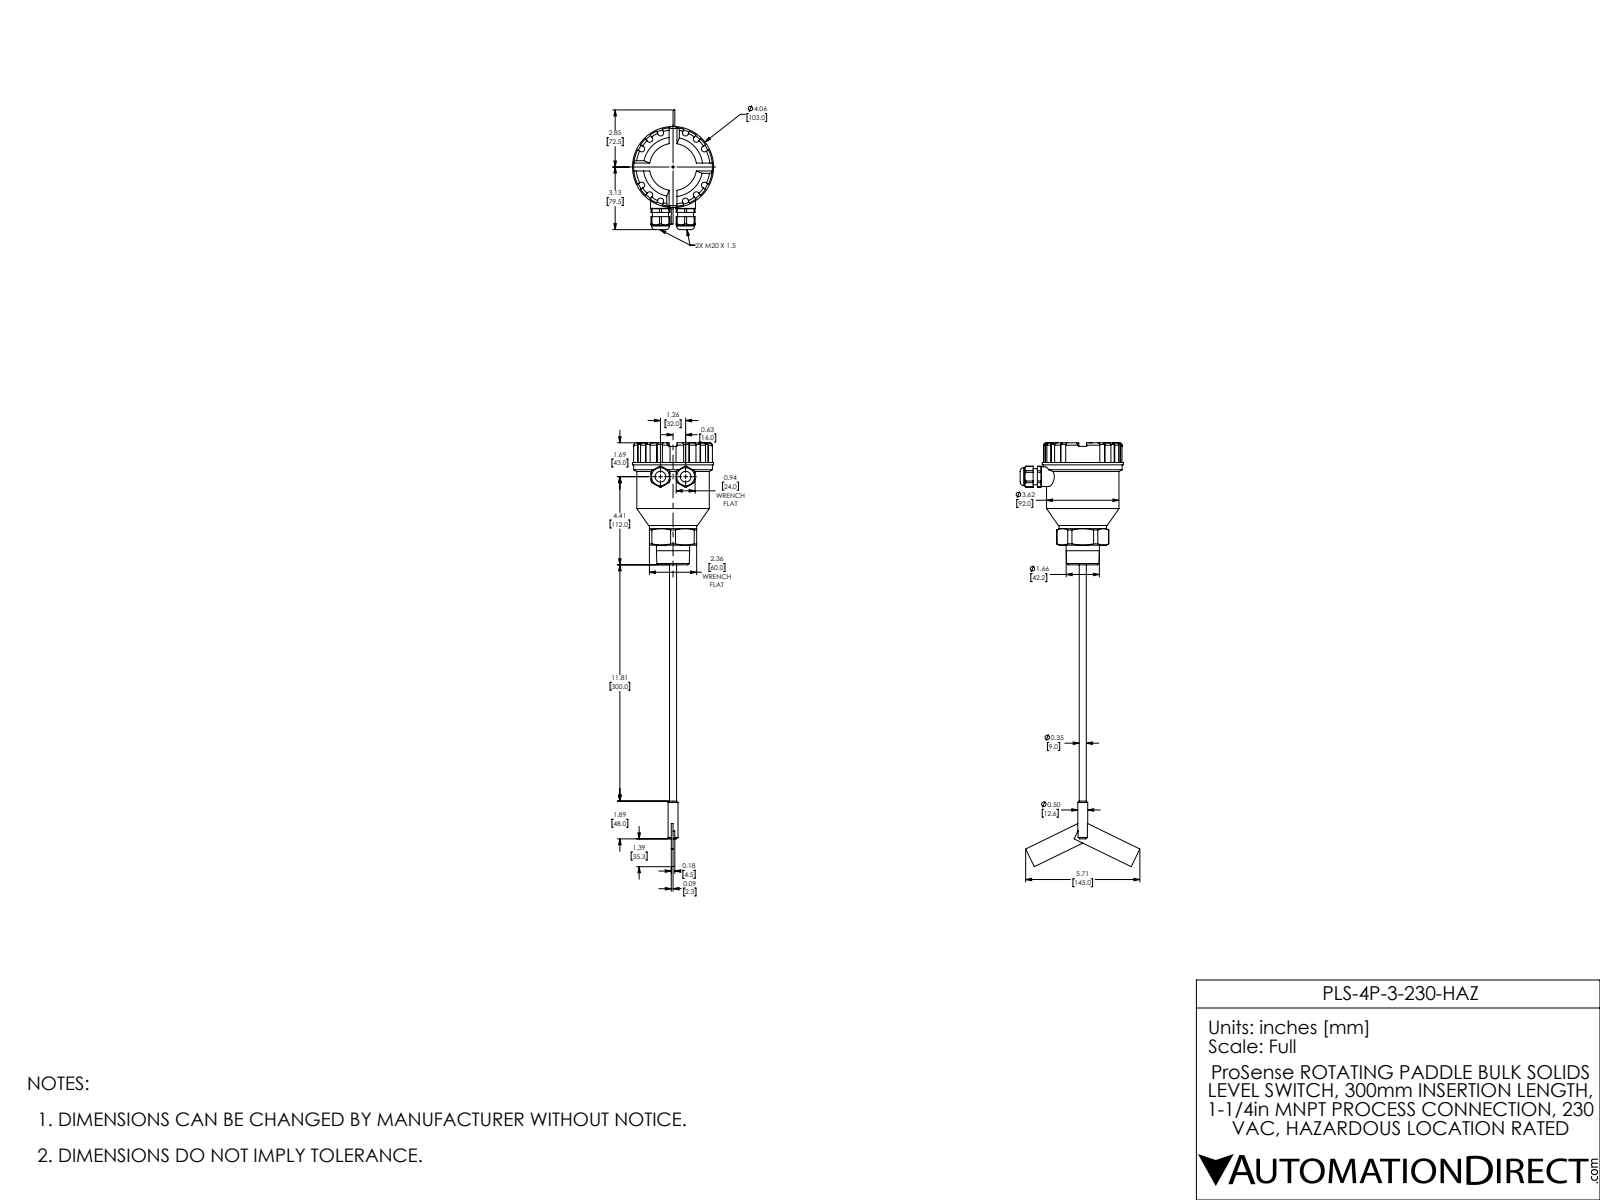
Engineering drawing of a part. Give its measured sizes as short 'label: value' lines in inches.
name: 300mm Shaft NC
written by: SolidWorks 2017 (AUTOMOTIVE_DESIGN)
unit: in
bodies: 1 solid, 279 faces (112 planar, 112 cylindrical, 55 other)
size: 21.193 × 5.984 × 4.055
volume: 51.99 in³; area: 120.4 in²
bosses: 2× ⌀0.984, 2× ⌀0.898, 2× ⌀0.803, 1× ⌀4.055, 1× ⌀3.937, 1× ⌀3.622, 1× ⌀2.362, 1× ⌀1.66
rounds: 12× R0.15, 2× R0.52, 1× R1.299, 1× R1.929
face distances: 0.089, 0.177, 5.118, 0.984, 2.362, 4.941, 1.093, 1.181, 1.27, 5.925
